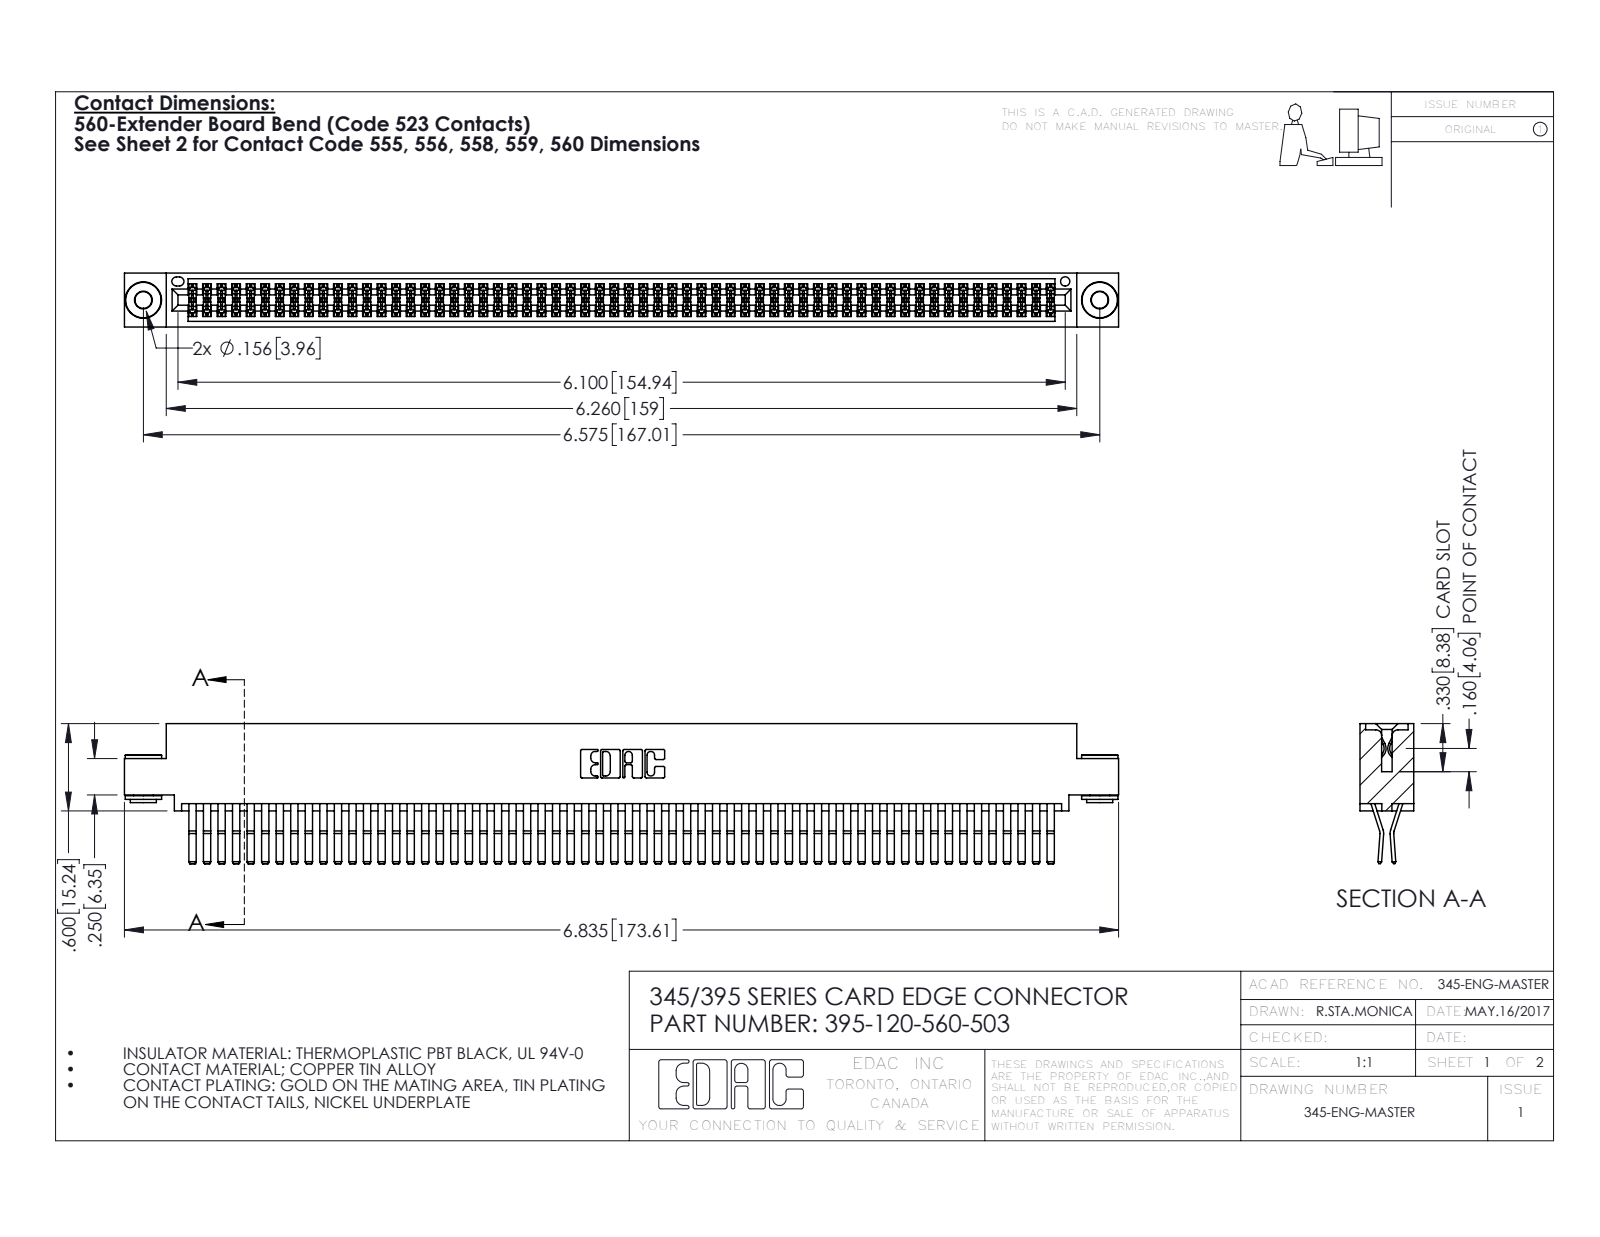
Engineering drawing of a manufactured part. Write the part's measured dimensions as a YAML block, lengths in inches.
part_name: "345-250-002_345-250-002-102; 345 Part_0.110 Offset - 0.156 Dia-TH; 345-292-001_560 Tail; 395-120-560-503"
step_written_by: "SolidWorks 2016 (CONFIG_CONTROL_DESIGN)"
units: inches
bodies: {solids: 123, faces: 6408, planar: 4054, cylindrical: 2346, other: 8}
overall_size: [6.835, 0.962, 0.37]
volume: 1.084
surface_area: 44.84
round_holes:
  - {diameter: 0.116, count: 2}
  - {diameter: 0.156, count: 2}
  - {diameter: 0.064, count: 1}
round_bosses_or_shafts:
  - {diameter: 0.25, count: 2}
  - {diameter: 0.18, count: 2}
  - {diameter: 0.136, count: 2}
partial_cylinders:
  - {radius: 0.006, count: 180}
  - {radius: 0.01, count: 22}
  - {radius: 0.007, count: 6}
  - {radius: 0.031, count: 6}
  - {radius: 0.026, count: 3}
  - {radius: 0.01, count: 2}
  - {radius: 0.014, count: 2}
  - {radius: 0.019, count: 2}
face_to_face_distances: [0.025, 0.072, 0.298, 0.37, 0.2, 0.098, 0.272, 0.225, 0.175, 0.149]
hole_center_spacings: [0.27, 6.339, 6.575]
